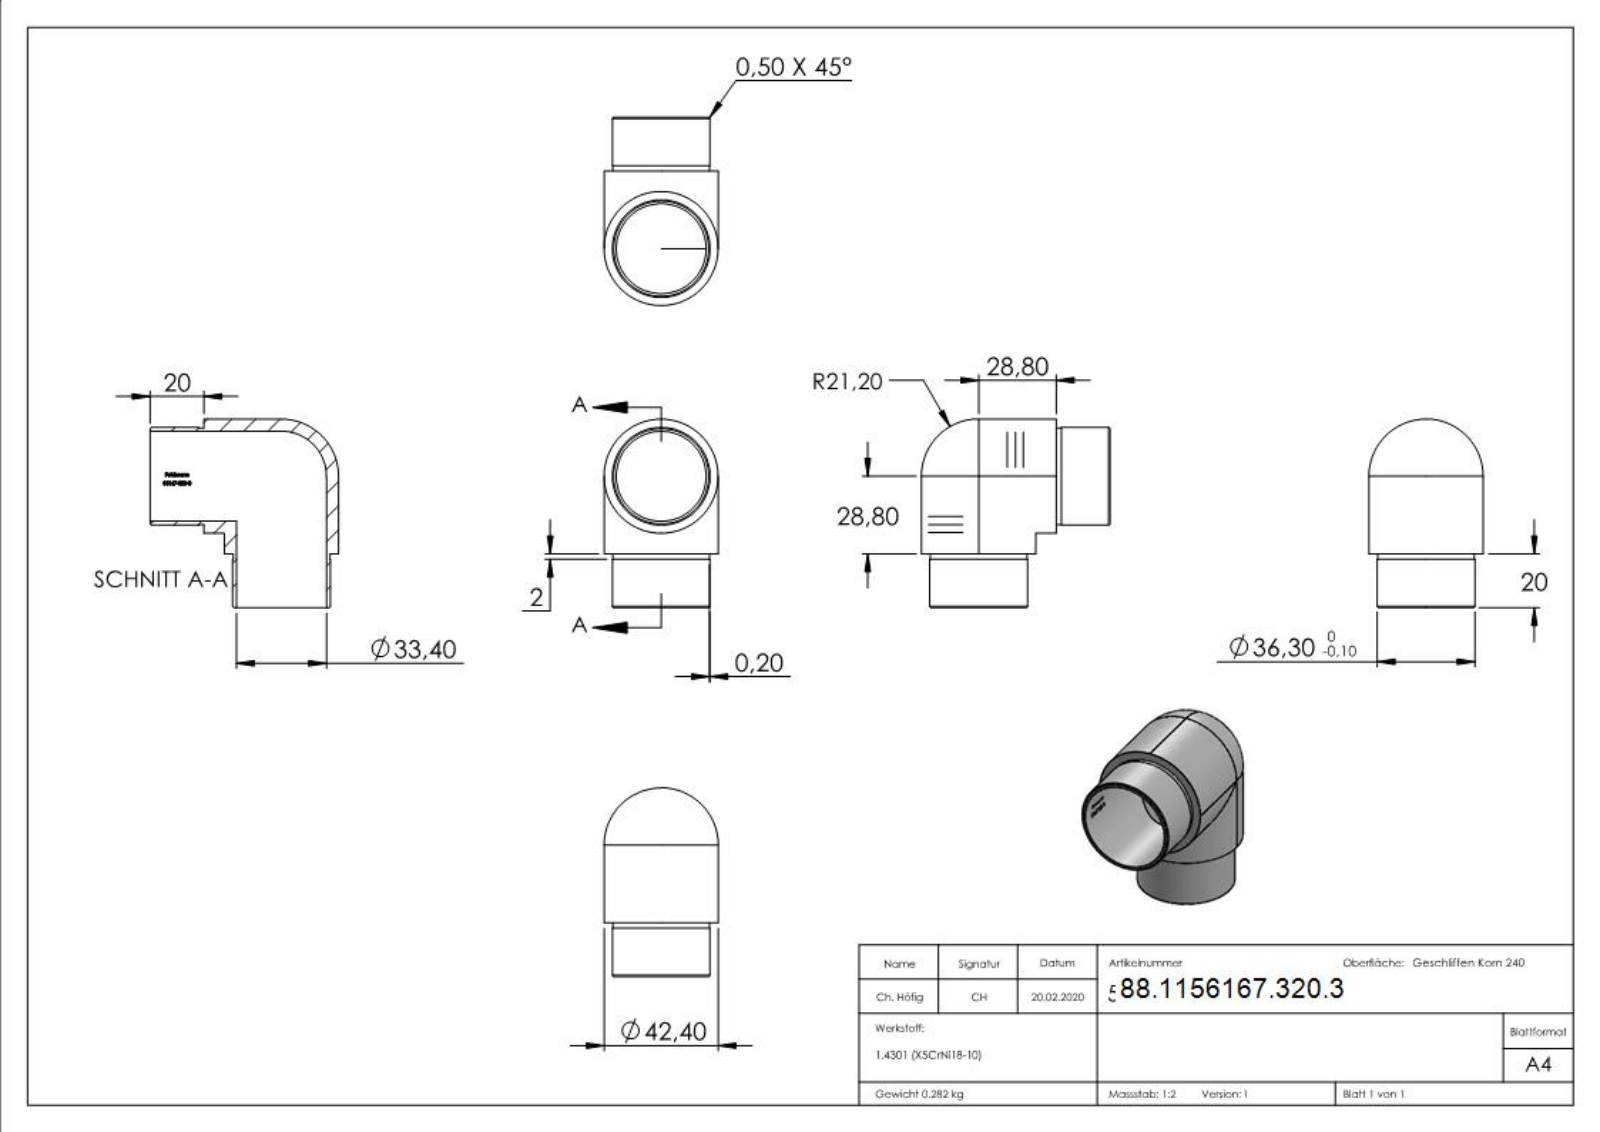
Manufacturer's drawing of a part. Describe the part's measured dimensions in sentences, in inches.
The part is named "56167-320-3". Its 3-D file was written by "SolidWorks 2015 (CONFIG_CONTROL_DESIGN)". It is 1 solid with 250 faces: 94 planar, 38 cylindrical and 118 other. Overall it measures 2.756 by 2.756 by 1.669 inches. Its volume is 2.178 cubic inches and its surface area 35.63 square inches. Round holes: 2 of diameter 1.315. Round bosses or shafts: 2 of diameter 1.669, 2 of diameter 1.429, 2 of diameter 1.413. Partial cylindrical surfaces (rounded edges, fillets, slot ends): 1 of radius 0.677. The main face-to-face distances are 0.787, 0.709, 0.079, 0.015, 0.05, 0.117, 0.167, 0.052, 0.144, 0.129.
